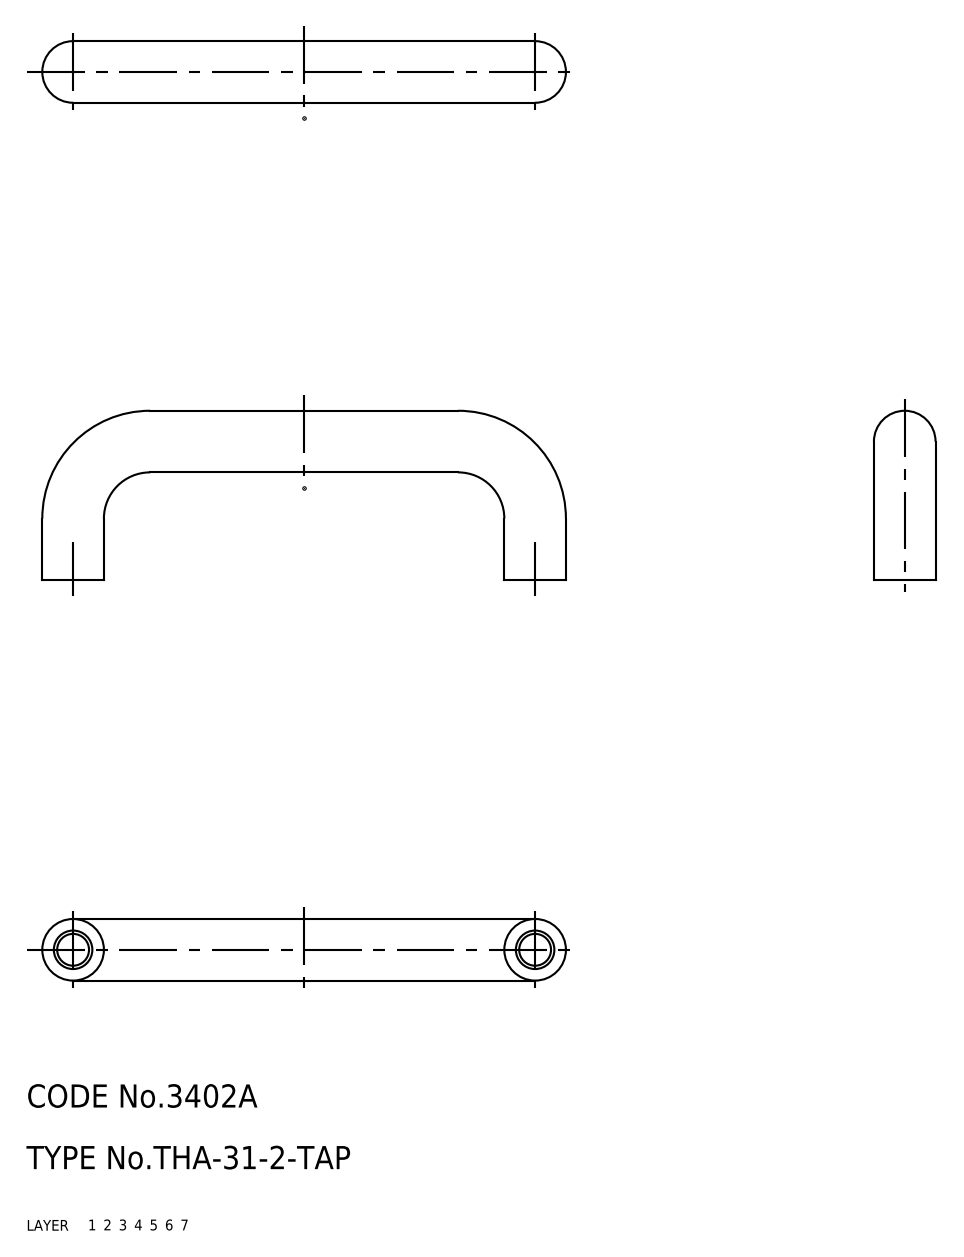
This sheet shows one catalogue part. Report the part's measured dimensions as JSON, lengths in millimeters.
{"part_name": "pull", "step_written_by": "CADfix (AUTOMOTIVE_DESIGN)", "units": "millimeters", "bodies": {"solids": 1, "faces": 18, "planar": 0, "cylindrical": 0, "other": 18}, "overall_size": [68, 22, 8], "volume_mm3": 4010, "surface_area_mm2": 2614}
